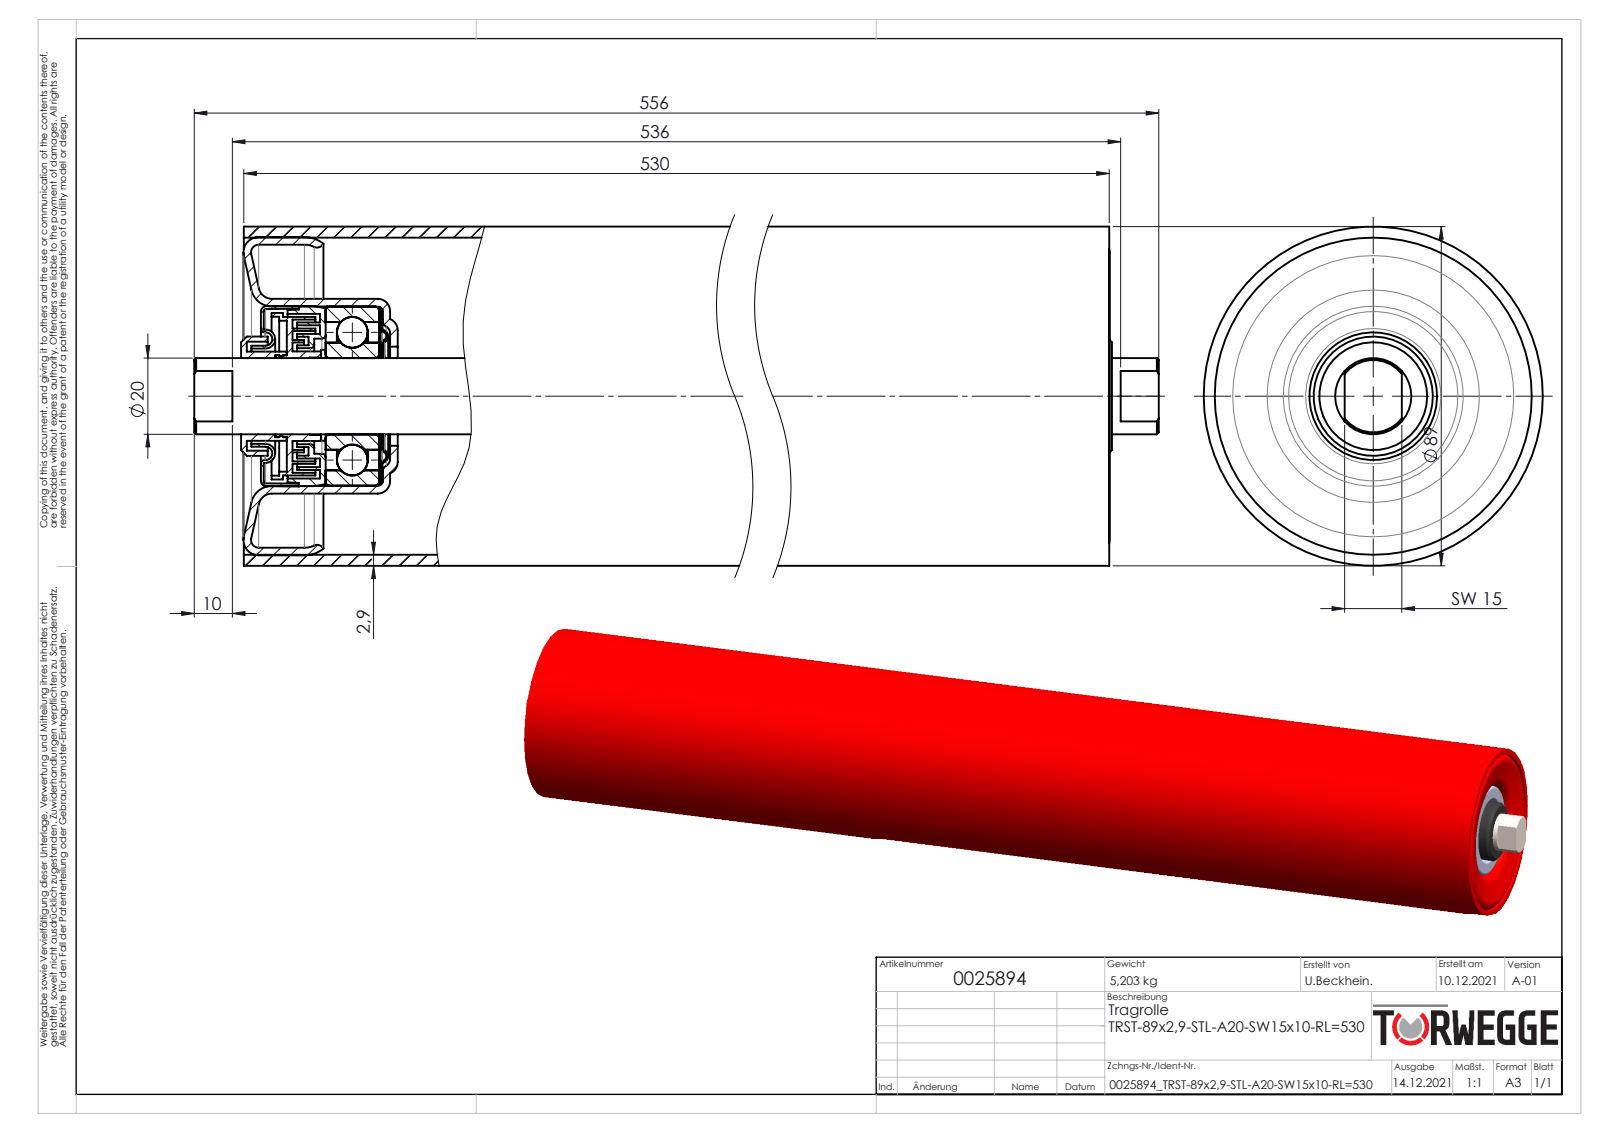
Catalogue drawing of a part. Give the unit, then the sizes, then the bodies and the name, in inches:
Units: inches
Overall size (bounding box): 21.89 × 3.504 × 3.504
Round holes (diameter × count): ⌀0.079 ×4, ⌀0.748 ×1, ⌀0.772 ×1, ⌀0.787 ×1, ⌀0.799 ×1, ⌀0.827 ×1, ⌀0.846 ×1, ⌀0.984 ×1, ⌀0.992 ×1, ⌀1.024 ×1, ⌀1.11 ×1, ⌀1.126 ×1
Round bosses / shafts (diameter × count): ⌀0.941 ×2, ⌀3.504 ×1, ⌀3.287 ×1, ⌀2.012 ×1, ⌀1.858 ×1, ⌀1.85 ×1, ⌀1.831 ×1, ⌀1.72 ×1
Partial cylindrical surfaces — rounded edges, fillets, slot ends (radius × count): R0.079 ×8, R0.531 ×1
Main face-to-face distances: 0.551, 18.623, 0.587, 18.587, 0.036, 18.035, 19.174, 0.402, 0.953, 0.989
Hole centre spacings: 0.452, 0.453, 0.888, 0.157, 0.157, 0.844, 0.905
Volume: 45.3 in³ · Surface area: 741.8 in²
Bodies: 24 solids, 606 faces (114 planar, 244 cylindrical, 248 other)
Part name (STEP PRODUCT): 0025894
STEP written by: SolidWorks 2020 (AUTOMOTIVE_DESIGN)
